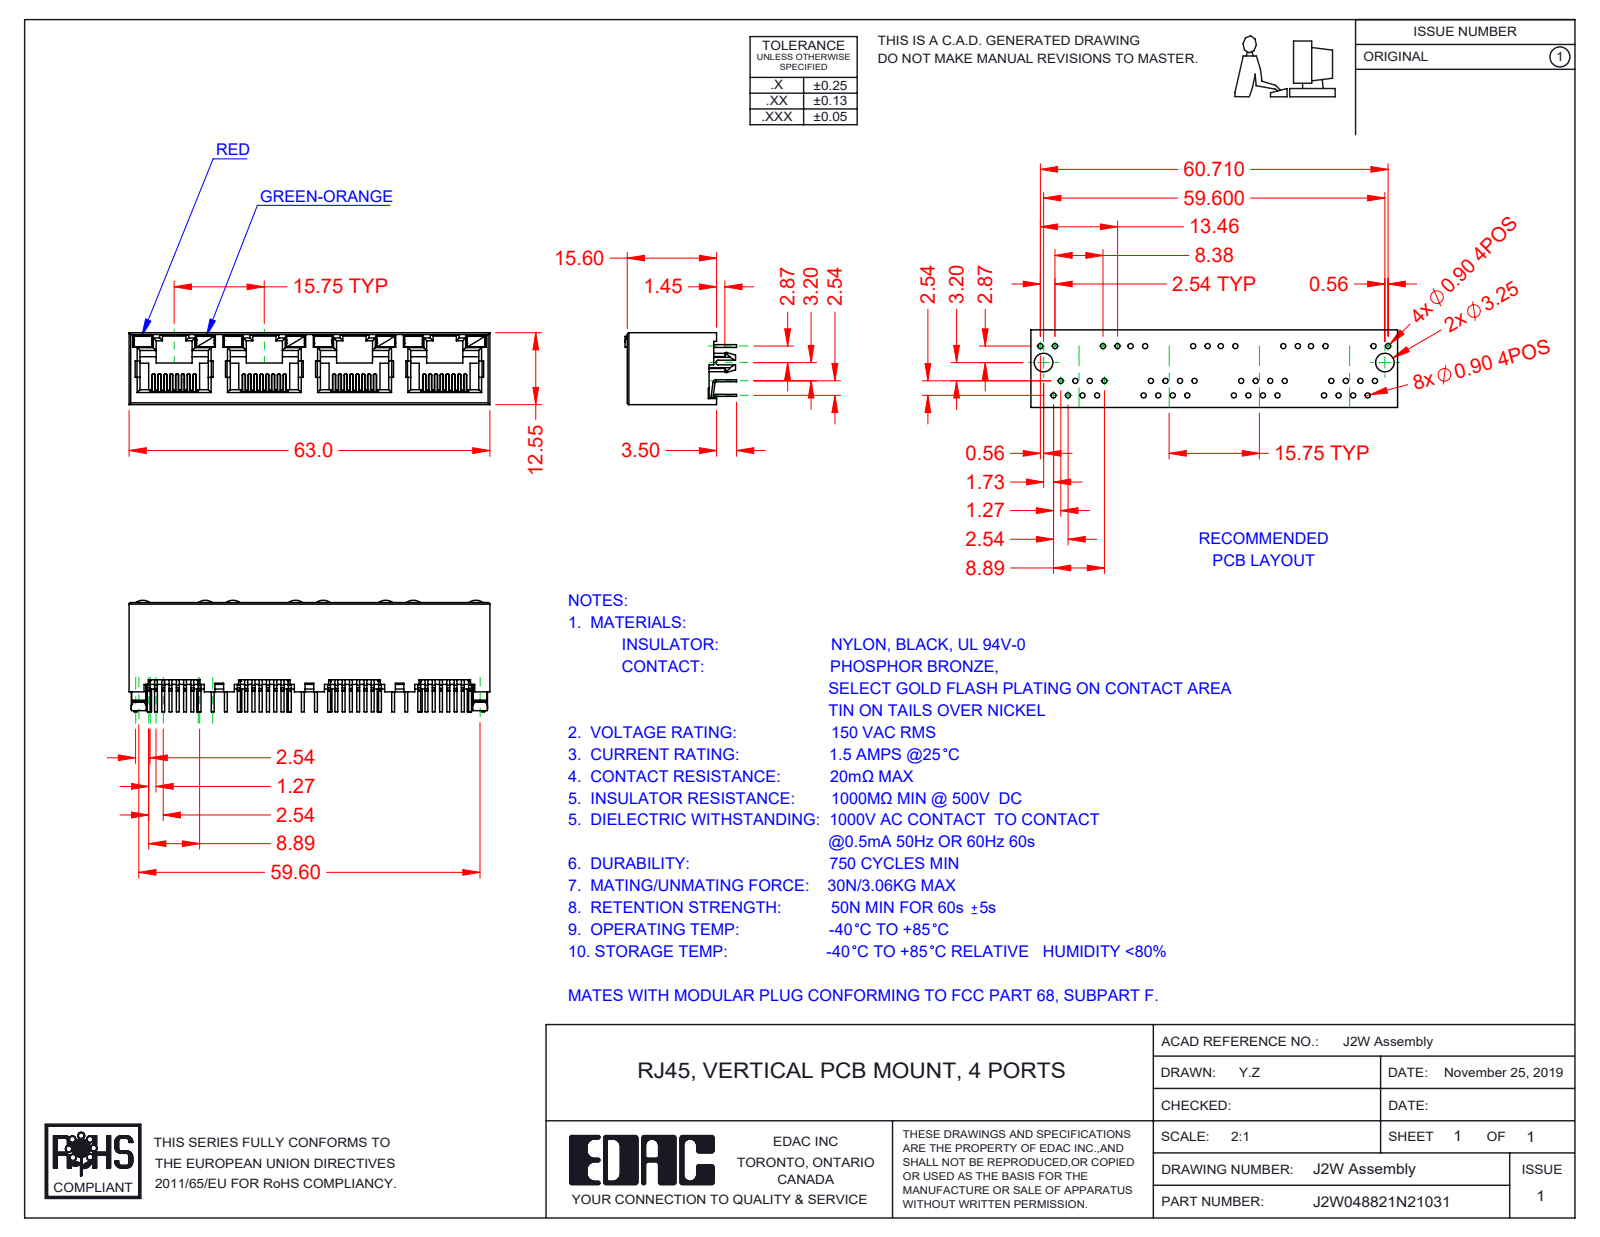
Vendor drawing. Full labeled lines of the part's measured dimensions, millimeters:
Part name (STEP PRODUCT): 2W Contacts; 2W Insulator; 2W Contact Lock; J2W048821N27131 (+2 more)
STEP written by: SolidWorks 2016 (CONFIG_CONTROL_DESIGN)
Units: millimetres
Bodies: 45 solids, 3139 faces (2600 planar, 481 cylindrical, 58 other)
Overall size (bounding box): 63 × 19.5 × 12.55
Volume: 5 335 mm³ · Surface area: 13 144 mm²
Partial cylindrical surfaces — rounded edges, fillets, slot ends (radius × count): R0.15 ×64, R0.2 ×29, R0.5 ×28, R0.3 ×14, R0.45 ×8, R2 ×8, R0.25 ×2, R1.5 ×2
Main face-to-face distances: 12.55, 11.9, 0.65, 15.75, 0.36, 1.5, 0.78, 0.6, 11.3, 31.5
